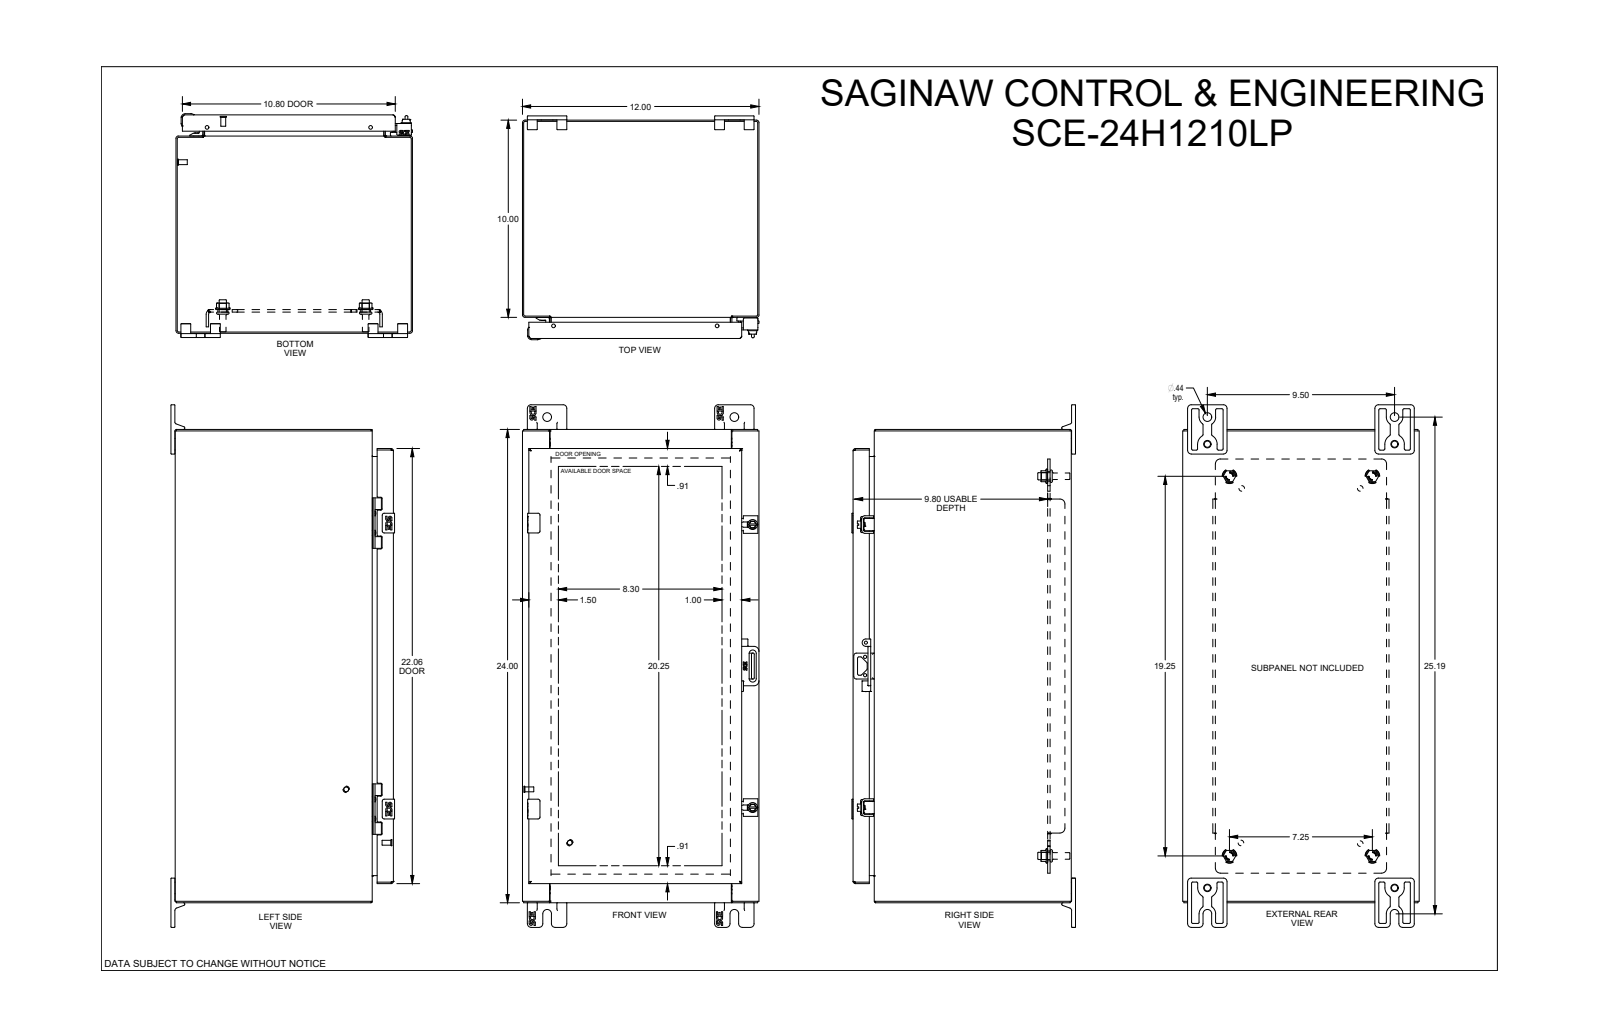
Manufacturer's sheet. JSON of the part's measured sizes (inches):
{"part_name": "SCE-24H1210LP", "step_written_by": "SolidWorks 2019 (CONFIG_CONTROL_DESIGN)", "units": "inches", "bodies": {"solids": 0, "faces": 3917, "planar": 1504, "cylindrical": 1128, "other": 1285}, "overall_size": [26.5, 12, 11.348], "round_holes": [[0.172, 4], [0.205, 4], [0.218, 4], [0.244, 4], [0.266, 4], [0.281, 4], [0.31, 4], [0.312, 4], [0.367, 4], [0.375, 4], [0.437, 4], [0.5, 4]], "round_bosses_or_shafts": [[0.17, 7], [0.25, 6], [0.248, 5], [0.59, 4], [0.376, 4], [0.366, 4], [0.332, 4], [0.24, 4]], "partial_cylinders_radius": [[0.025, 125], [0.01, 114], [0.015, 56], [0.03, 37], [0.062, 35], [0.06, 30], [0.063, 28], [0.185, 21]], "face_to_face_distances": [0.075, 11.925, 0.075, 10.998, 10.923, 23.925, 12, 11.85, 11.073, 10.998], "hole_center_spacings": [14.5, 0.02, 0.493, 0.875, 0.985, 1.977, 8.531, 20.905]}
